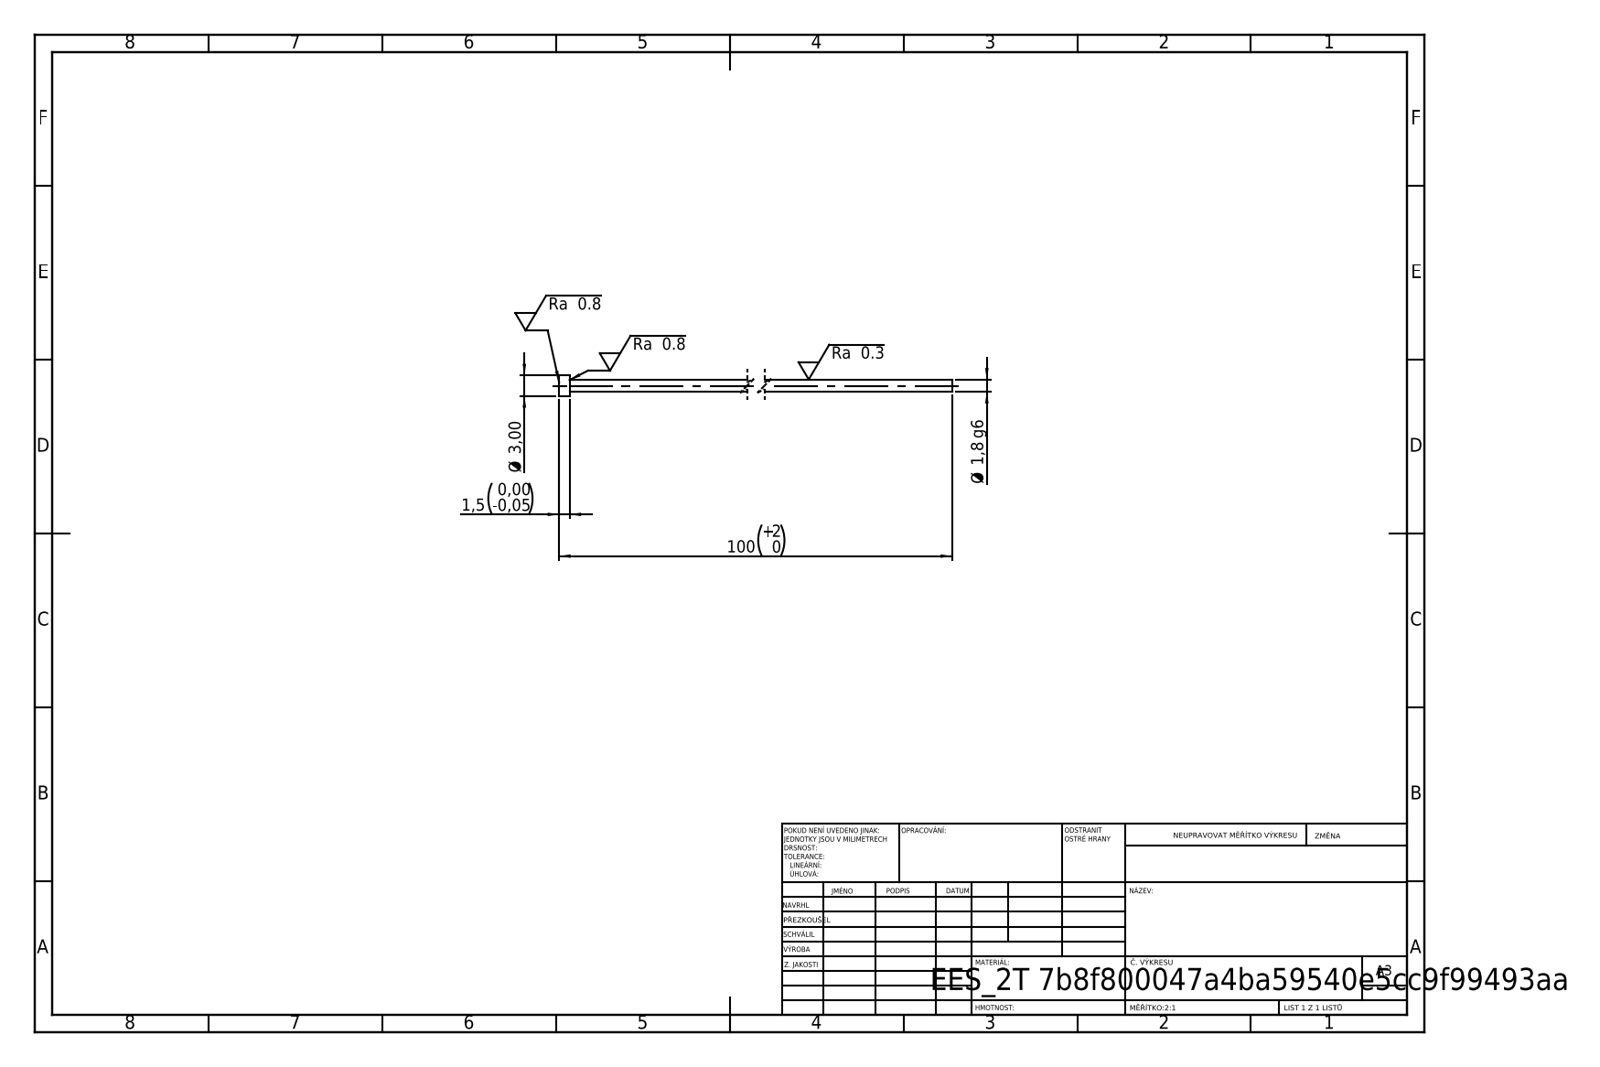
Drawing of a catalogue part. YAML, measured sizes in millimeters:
step_written_by: "SolidWorks 2019 (CONFIG_CONTROL_DESIGN)"
units: millimeters
bodies: {solids: 1, faces: 7, planar: 3, cylindrical: 4, other: 0}
overall_size: [100, 3, 3]
volume: 261
surface_area: 585
round_bosses_or_shafts:
  - {diameter: 3, count: 1}
  - {diameter: 1.8, count: 1}
face_to_face_distances: [1.5, 100, 98.5]
